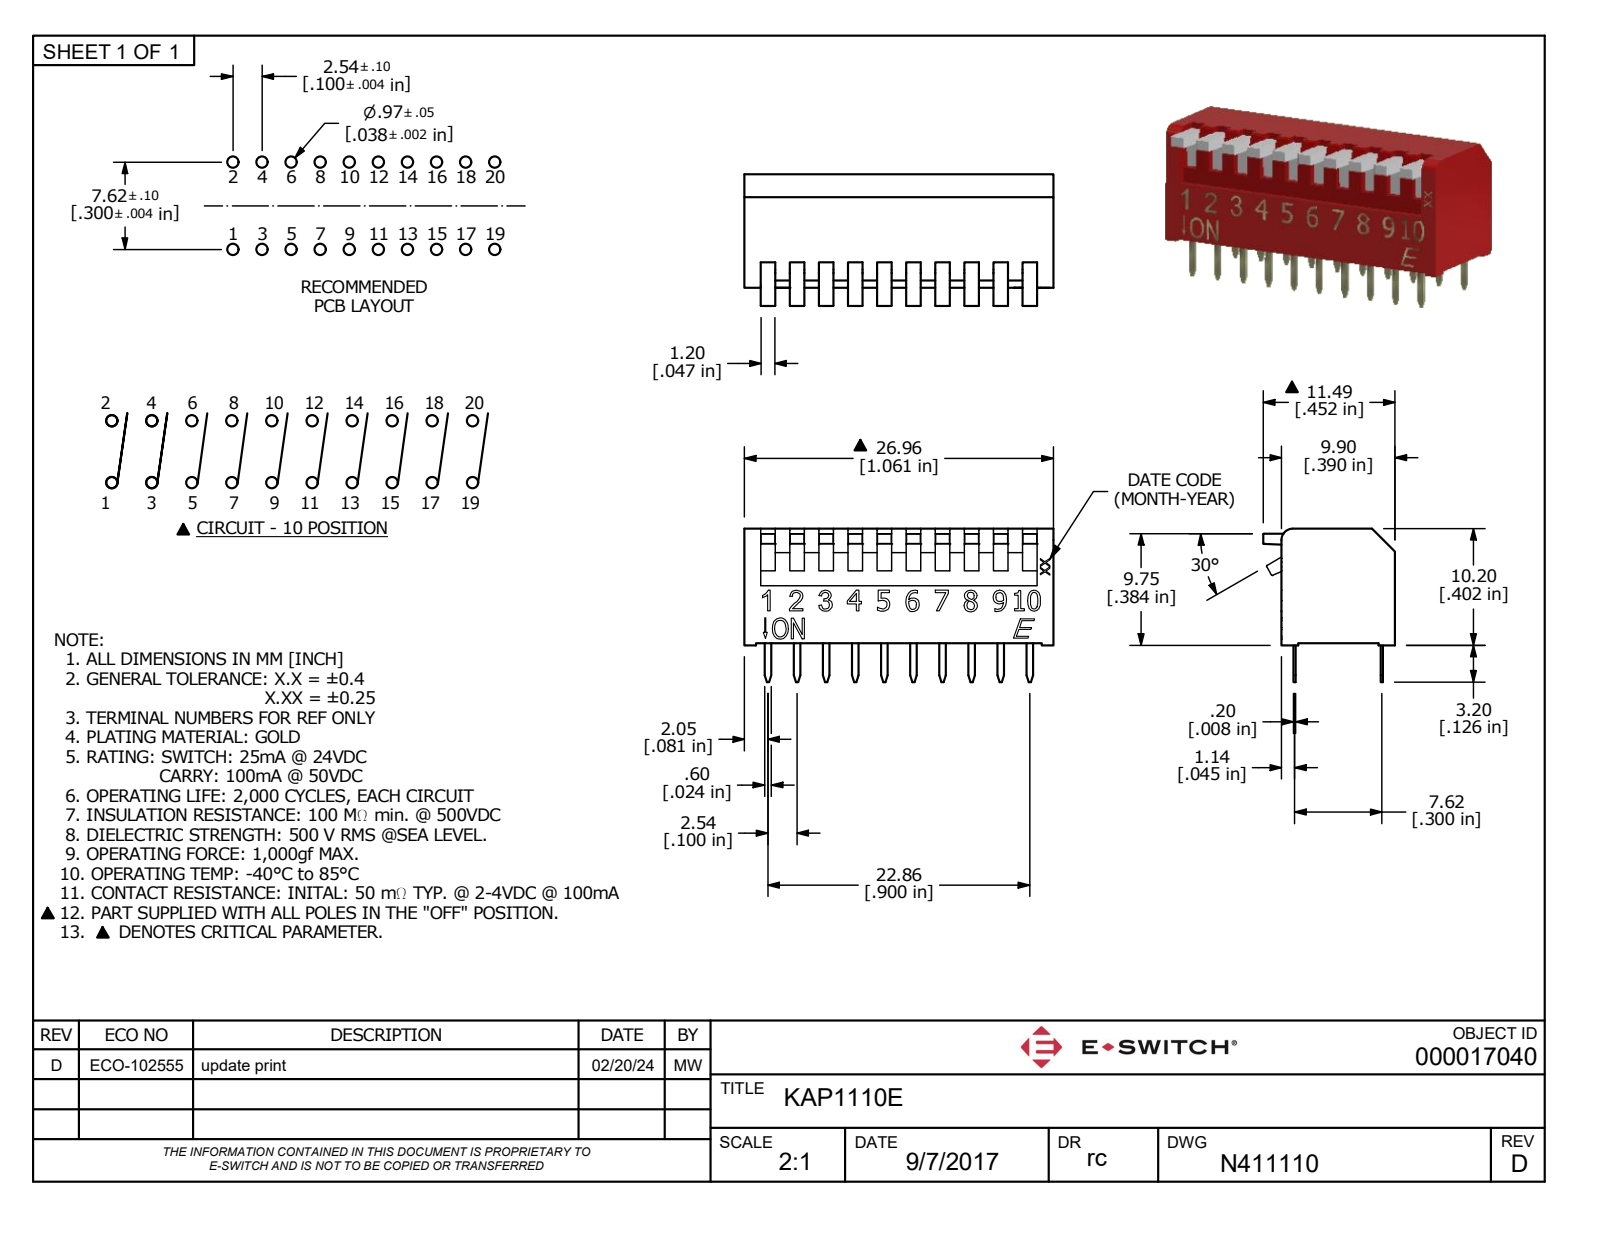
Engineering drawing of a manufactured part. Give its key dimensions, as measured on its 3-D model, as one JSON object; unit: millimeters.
{"part_name": "P:\\\\E-Switch Secure\\\\3D_MODELS_STP_FORMAT\\\\KAP1110E.stp", "step_written_by": "ACIS (CONFIG_CONTROL_DESIGN)", "units": "millimeters", "bodies": {"solids": 21, "faces": 641, "planar": 502, "cylindrical": 31, "other": 108}, "overall_size": [26.9, 13.6, 12.6], "volume_mm3": 2750, "surface_area_mm2": 1677, "partial_cylinders_radius": [[0.3, 2], [1, 1], [6.8, 1]], "face_to_face_distances": [10, 10.8, 7.6, 2.5, 26.9, 5.1, 10.2, 0.7, 10.2, 6.3]}
